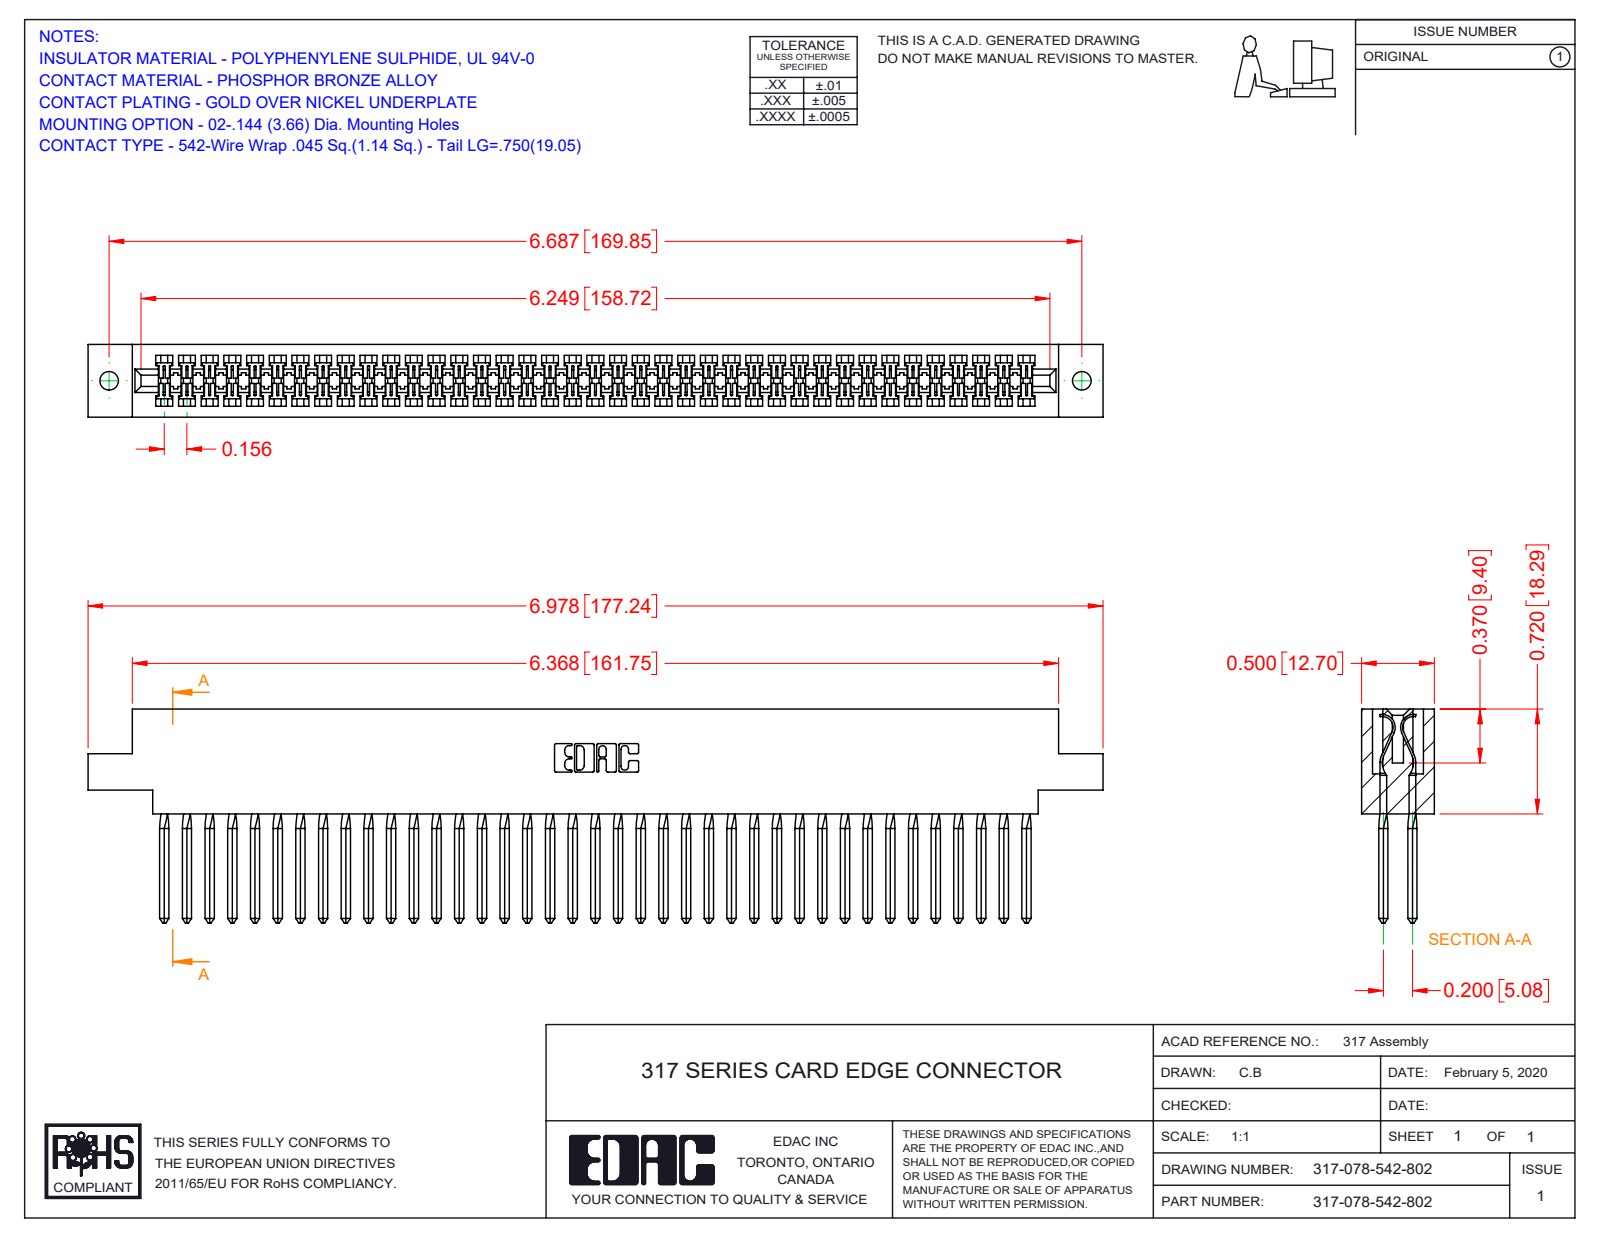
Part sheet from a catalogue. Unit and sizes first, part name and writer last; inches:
Units: inches
Overall size (bounding box): 6.978 × 1.47 × 0.5
Round holes (diameter × count): ⌀0.128 ×2
Partial cylindrical surfaces — rounded edges, fillets, slot ends (radius × count): R0.006 ×156, R0.01 ×22, R0.007 ×6, R0.031 ×6, R0.026 ×3, R0.074 ×2, R0.089 ×2, R0.1 ×2
Main face-to-face distances: 0.5, 0.075, 0.425, 0.35, 0.2, 0.046, 0.128, 0.372, 0.052, 0.297
Hole centre spacings: 6.687
Volume: 1.763 in³ · Surface area: 61.71 in²
Bodies: 79 solids, 4548 faces (3646 planar, 590 cylindrical, 312 other)
Part name (STEP PRODUCT): 317-290-003_542; 317-078-542-802; 317 Part_.144 Dia
STEP written by: SolidWorks 2016 (CONFIG_CONTROL_DESIGN)
